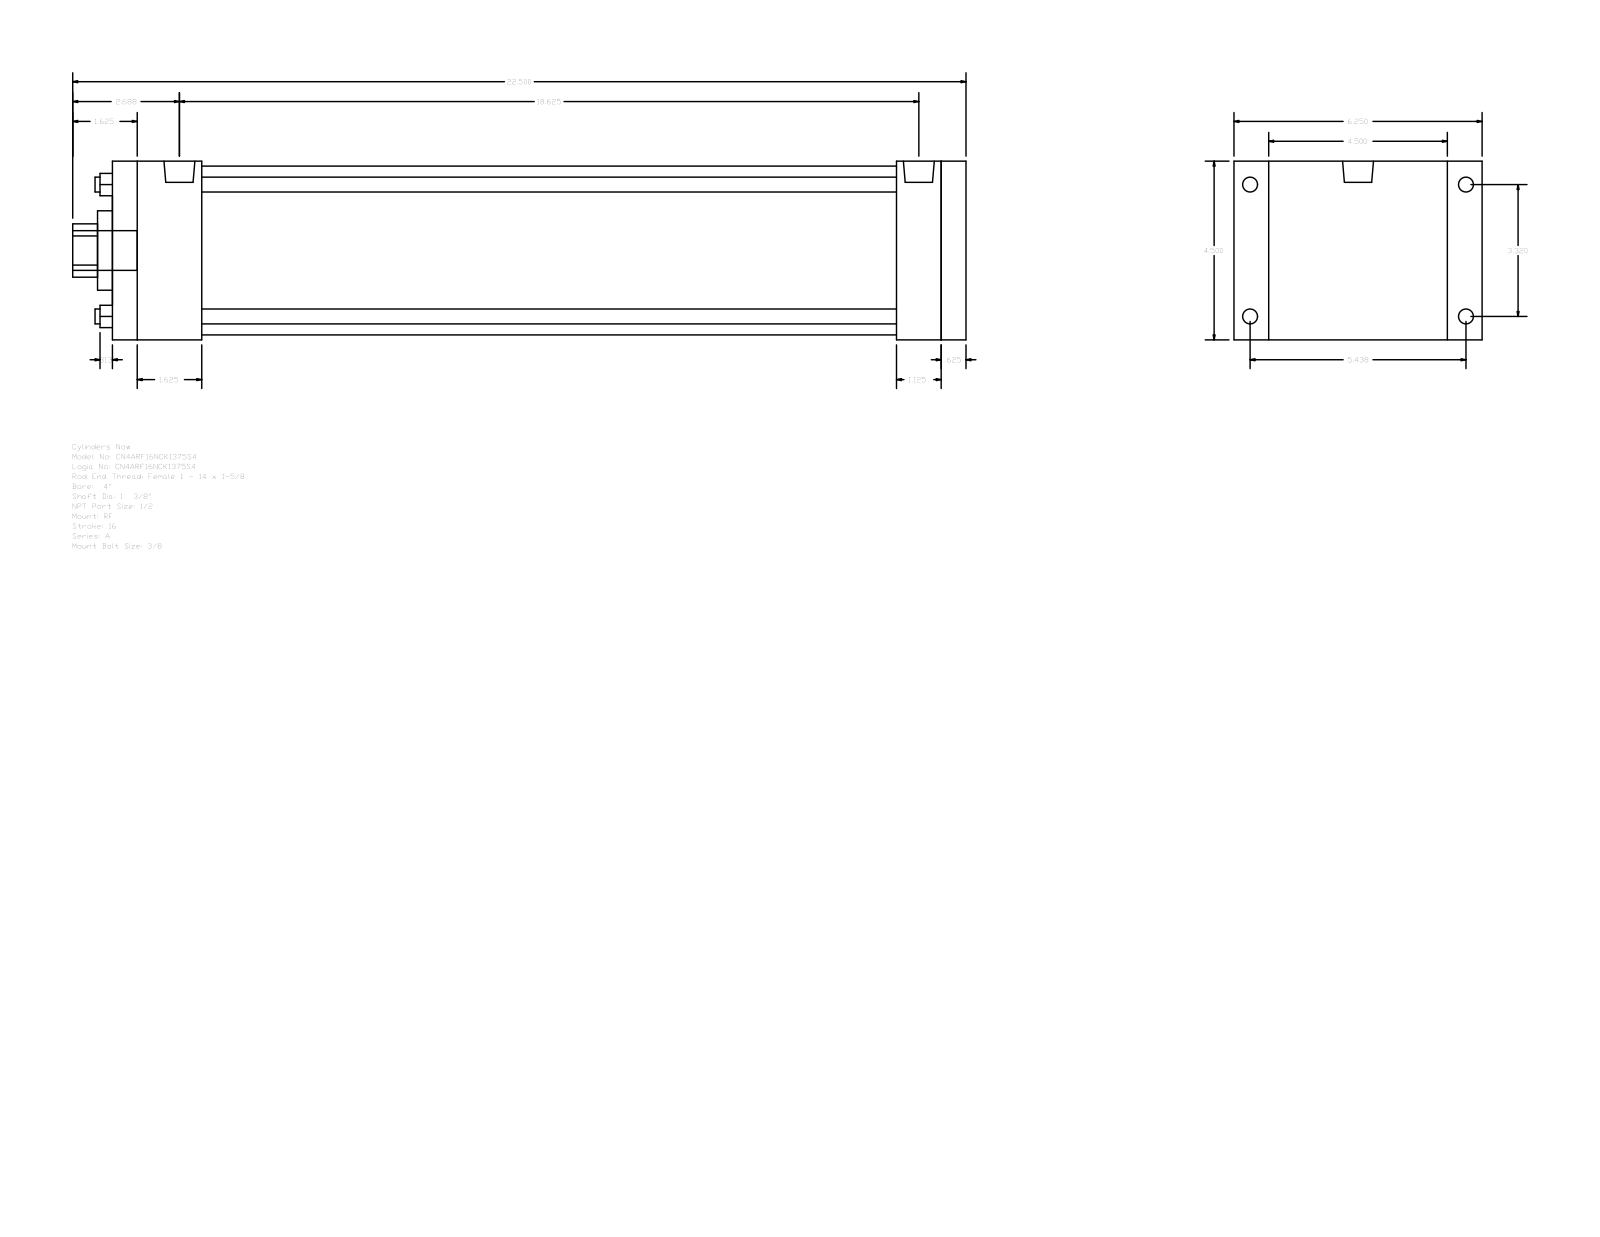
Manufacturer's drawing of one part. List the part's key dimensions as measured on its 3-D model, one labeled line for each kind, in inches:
Part name (STEP PRODUCT): A_RF__0400_1.375
STEP written by: GSSL Pune (CONFIG_CONTROL_DESIGN)
Units: inches
Bodies: 0 solids, 92 faces (64 planar, 28 cylindrical, 0 other)
Overall size (bounding box): 22.5 × 6.25 × 4.5
Round holes (diameter × count): ⌀0.375 ×4, ⌀1.375 ×1, ⌀2 ×1, ⌀4.25 ×1
Round bosses / shafts (diameter × count): ⌀0.375 ×4, ⌀0.344 ×4, ⌀0.778 ×2, ⌀1 ×1
Partial cylindrical surfaces — rounded edges, fillets, slot ends (radius × count): R0.672 ×1
Main face-to-face distances: 4.5, 21.5, 0.625, 20.875, 1.125, 0.875, 5.375, 19.75, 1.75, 2.25
Hole centre spacings: 2.347, 3.32, 4.695
